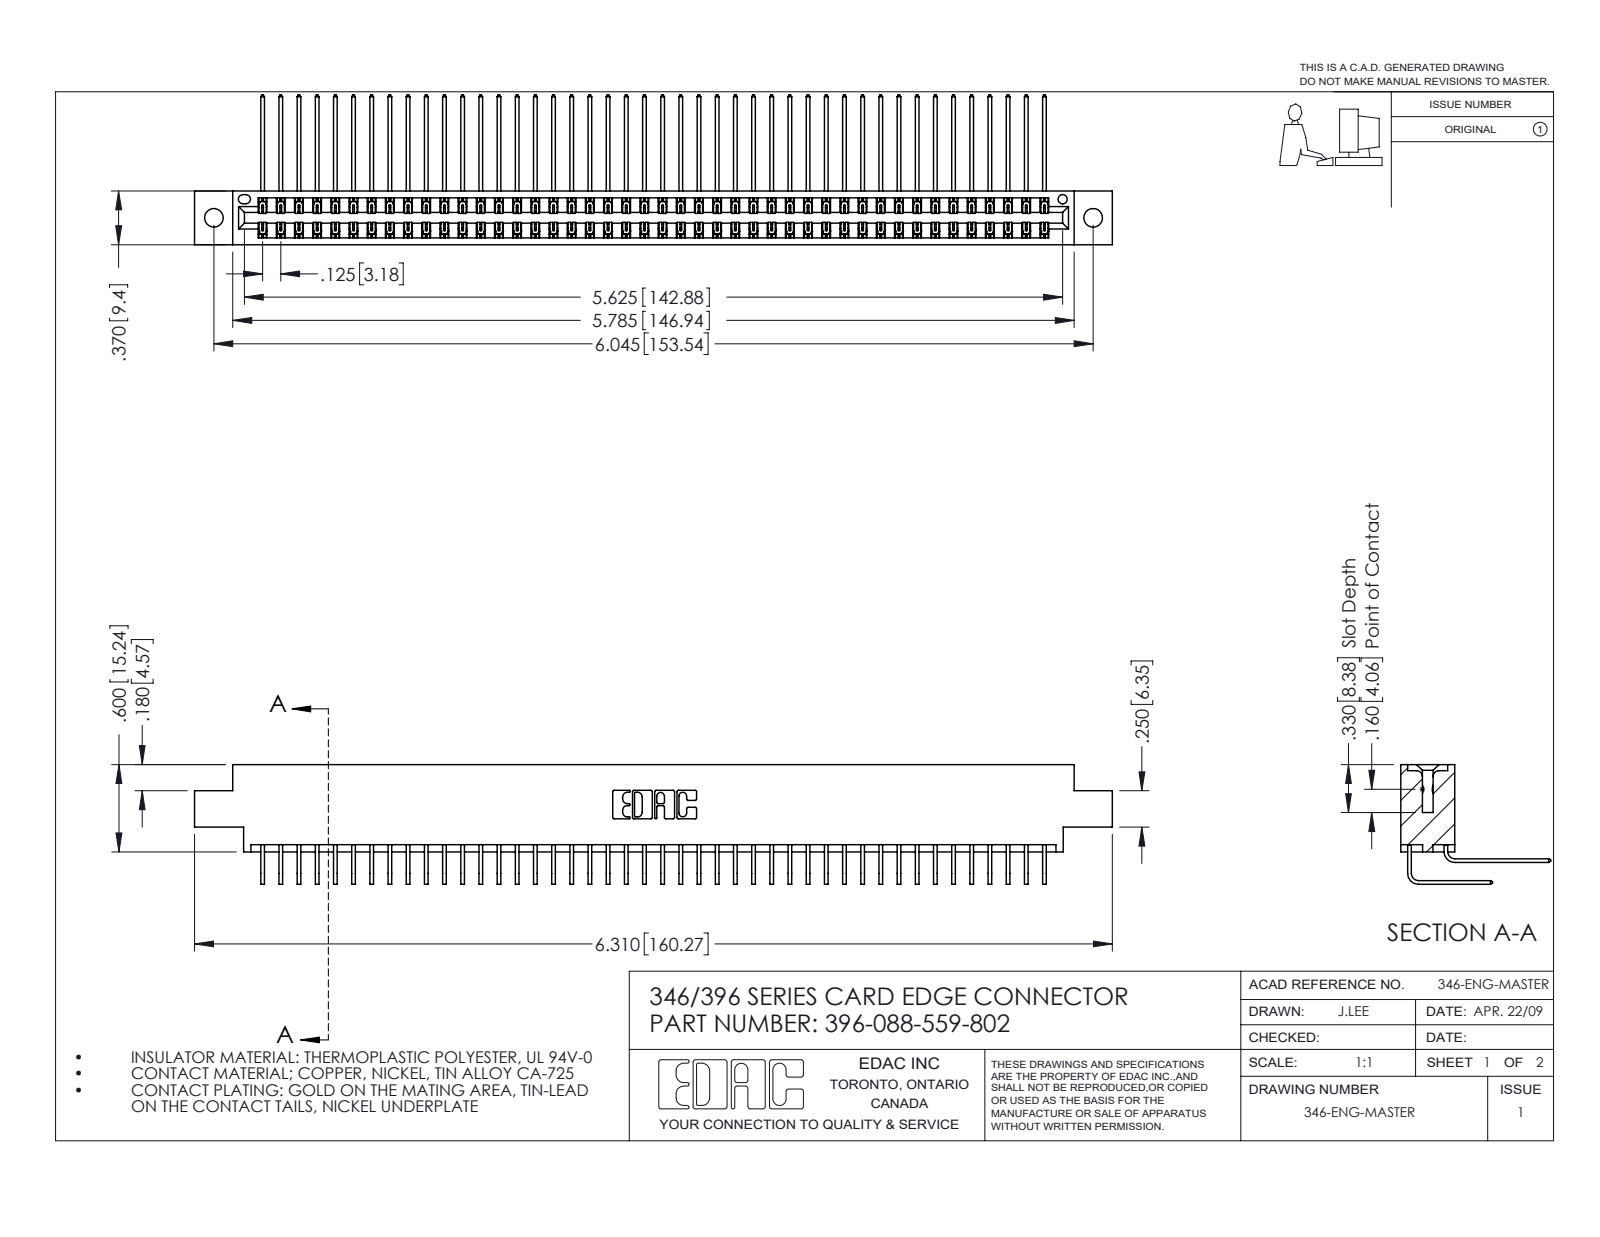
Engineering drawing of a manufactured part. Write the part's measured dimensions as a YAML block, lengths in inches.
part_name: "345-292-001_558 559 Tail - 1; 346 Part_0.170 Offset - 0.128 Dia; 345-292-001_559 Tail - 2; 396-088-559-802"
step_written_by: "SolidWorks 2016 (CONFIG_CONTROL_DESIGN)"
units: inches
bodies: {solids: 89, faces: 4878, planar: 3336, cylindrical: 1542, other: 0}
overall_size: [6.31, 1.03, 0.823]
volume: 0.974
surface_area: 37.69
round_holes:
  - {diameter: 0.128, count: 2}
  - {diameter: 0.064, count: 1}
partial_cylinders:
  - {radius: 0.006, count: 132}
  - {radius: 0.01, count: 22}
  - {radius: 0.007, count: 6}
  - {radius: 0.031, count: 6}
  - {radius: 0.026, count: 3}
  - {radius: 0.014, count: 2}
  - {radius: 0.022, count: 2}
  - {radius: 0.024, count: 2}
face_to_face_distances: [0.048, 0.322, 0.025, 0.37, 0.25, 0.072, 0.298, 0.275, 0.148, 0.222]
hole_center_spacings: [0.246, 5.836, 6.045]
